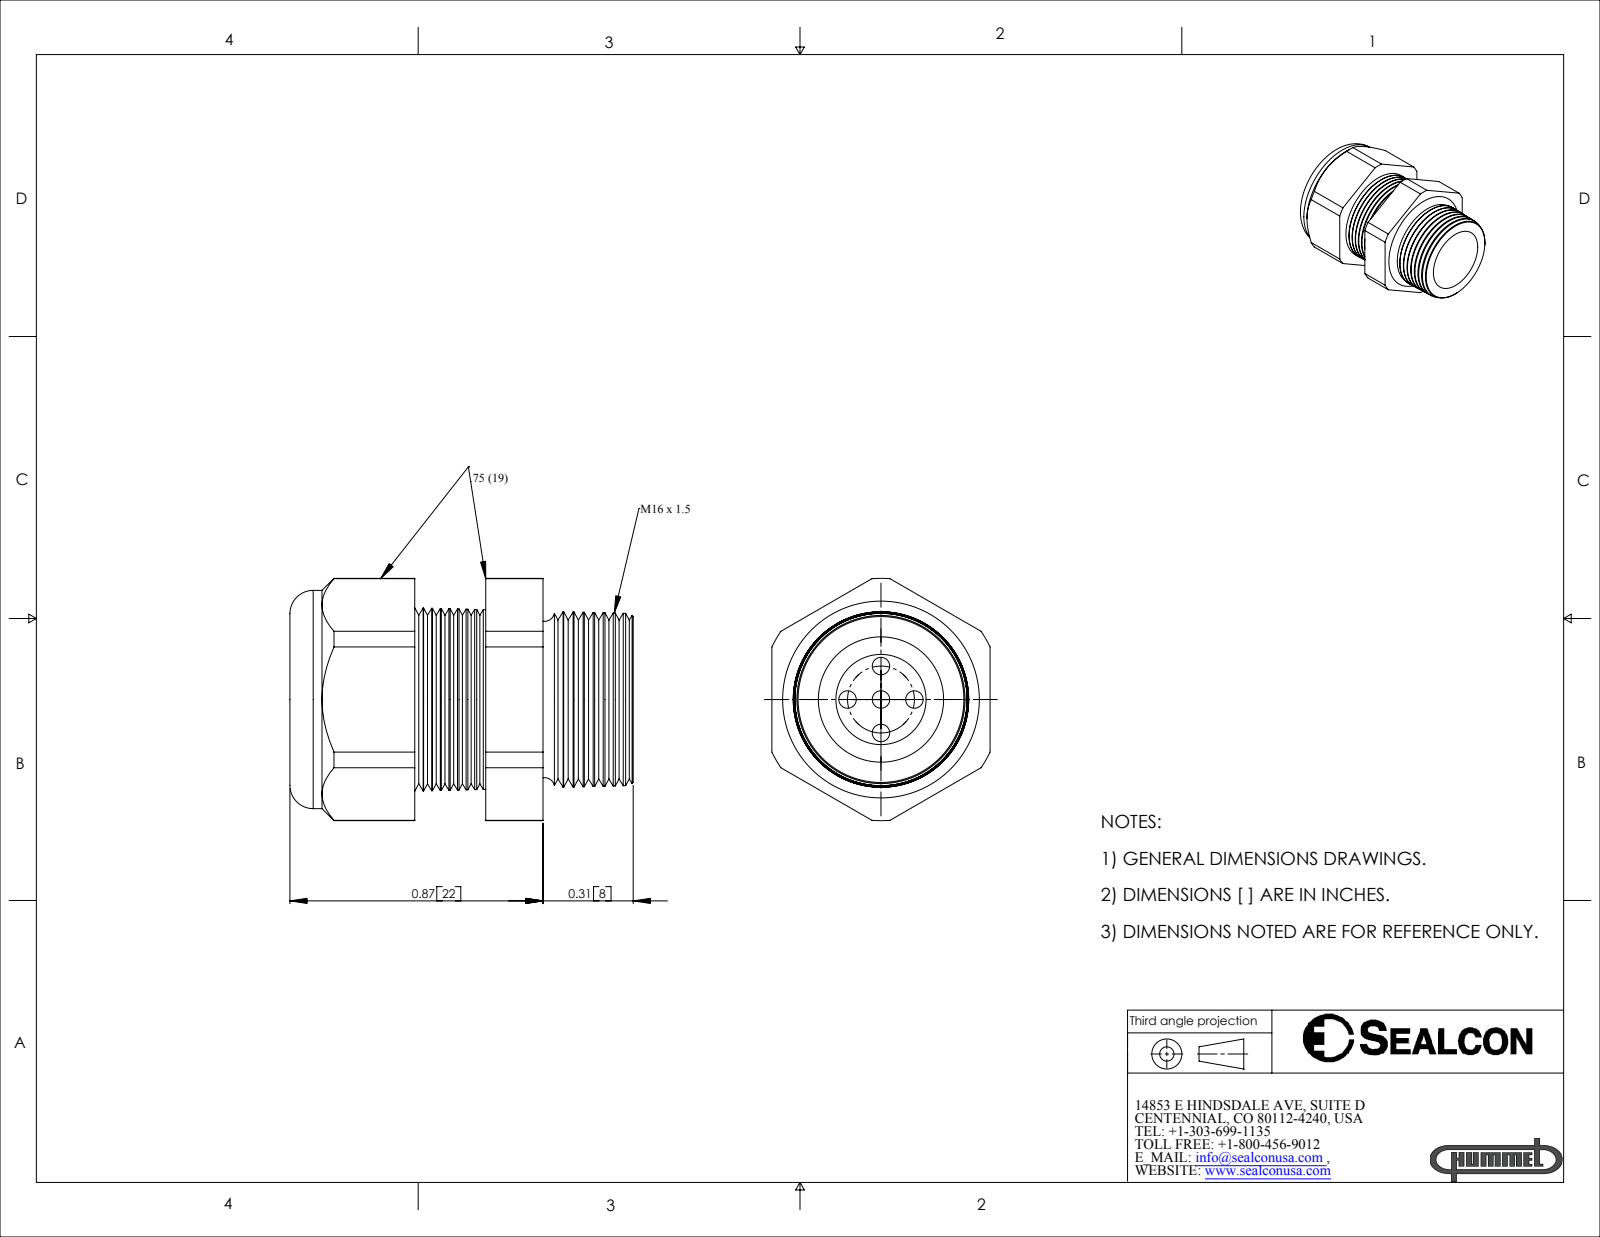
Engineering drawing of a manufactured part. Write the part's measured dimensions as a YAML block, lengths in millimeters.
part_name: "CD16M3-GY"
step_written_by: "SolidWorks 2007 (CONFIG_CONTROL_DESIGN)"
units: millimeters
bodies: {solids: 2, faces: 160, planar: 20, cylindrical: 30, other: 110}
overall_size: [30, 21.2, 19.1]
volume: 5510
surface_area: 4003
round_holes:
  - {diameter: 1.5, count: 5}
  - {diameter: 7.4, count: 1}
  - {diameter: 7.9, count: 1}
round_bosses_or_shafts:
  - {diameter: 19.1, count: 1}
partial_cylinders:
  - {radius: 10.6, count: 1}
face_to_face_distances: [19.1, 17.1, 19.1, 10.9, 6.2, 22.1, 11.2, 5, 30, 19.1]
hole_center_spacings: [2.9, 4.1, 5.8]
